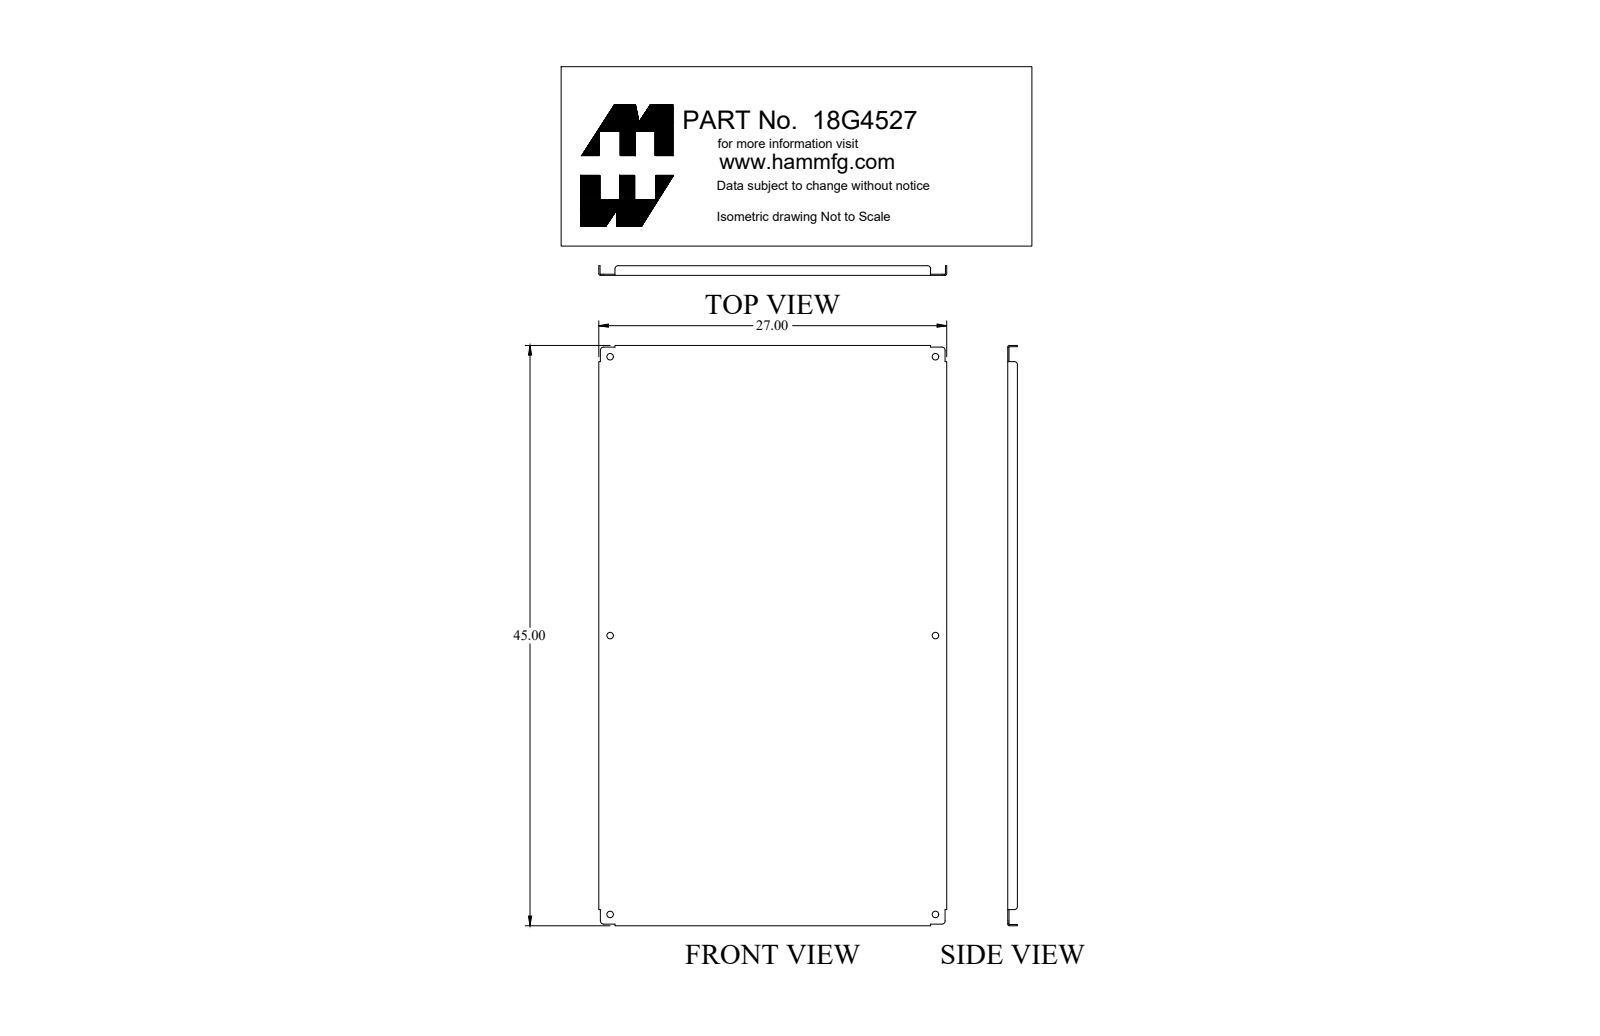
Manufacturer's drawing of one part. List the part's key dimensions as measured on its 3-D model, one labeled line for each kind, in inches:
Part name (STEP PRODUCT): 18G4527_Default
STEP written by: SolidWorks 2018 (CONFIG_CONTROL_DESIGN)
Units: inches
Bodies: 1 solid, 62 faces (30 planar, 32 cylindrical, 0 other)
Overall size (bounding box): 45 × 27 × 0.75
Volume: 123.1 in³ · Surface area: 2 606 in²
Round holes (diameter × count): ⌀0.5 ×6
Partial cylindrical surfaces — rounded edges, fillets, slot ends (radius × count): R0.25 ×8, R0.03 ×4, R0.125 ×4
Main face-to-face distances: 0.095, 26.905, 44.905, 27, 26.81, 45, 44.81, 0.75, 0.655, 0.125
Hole centre spacings: 21.625, 33.244, 25.25, 43.25, 50.081
